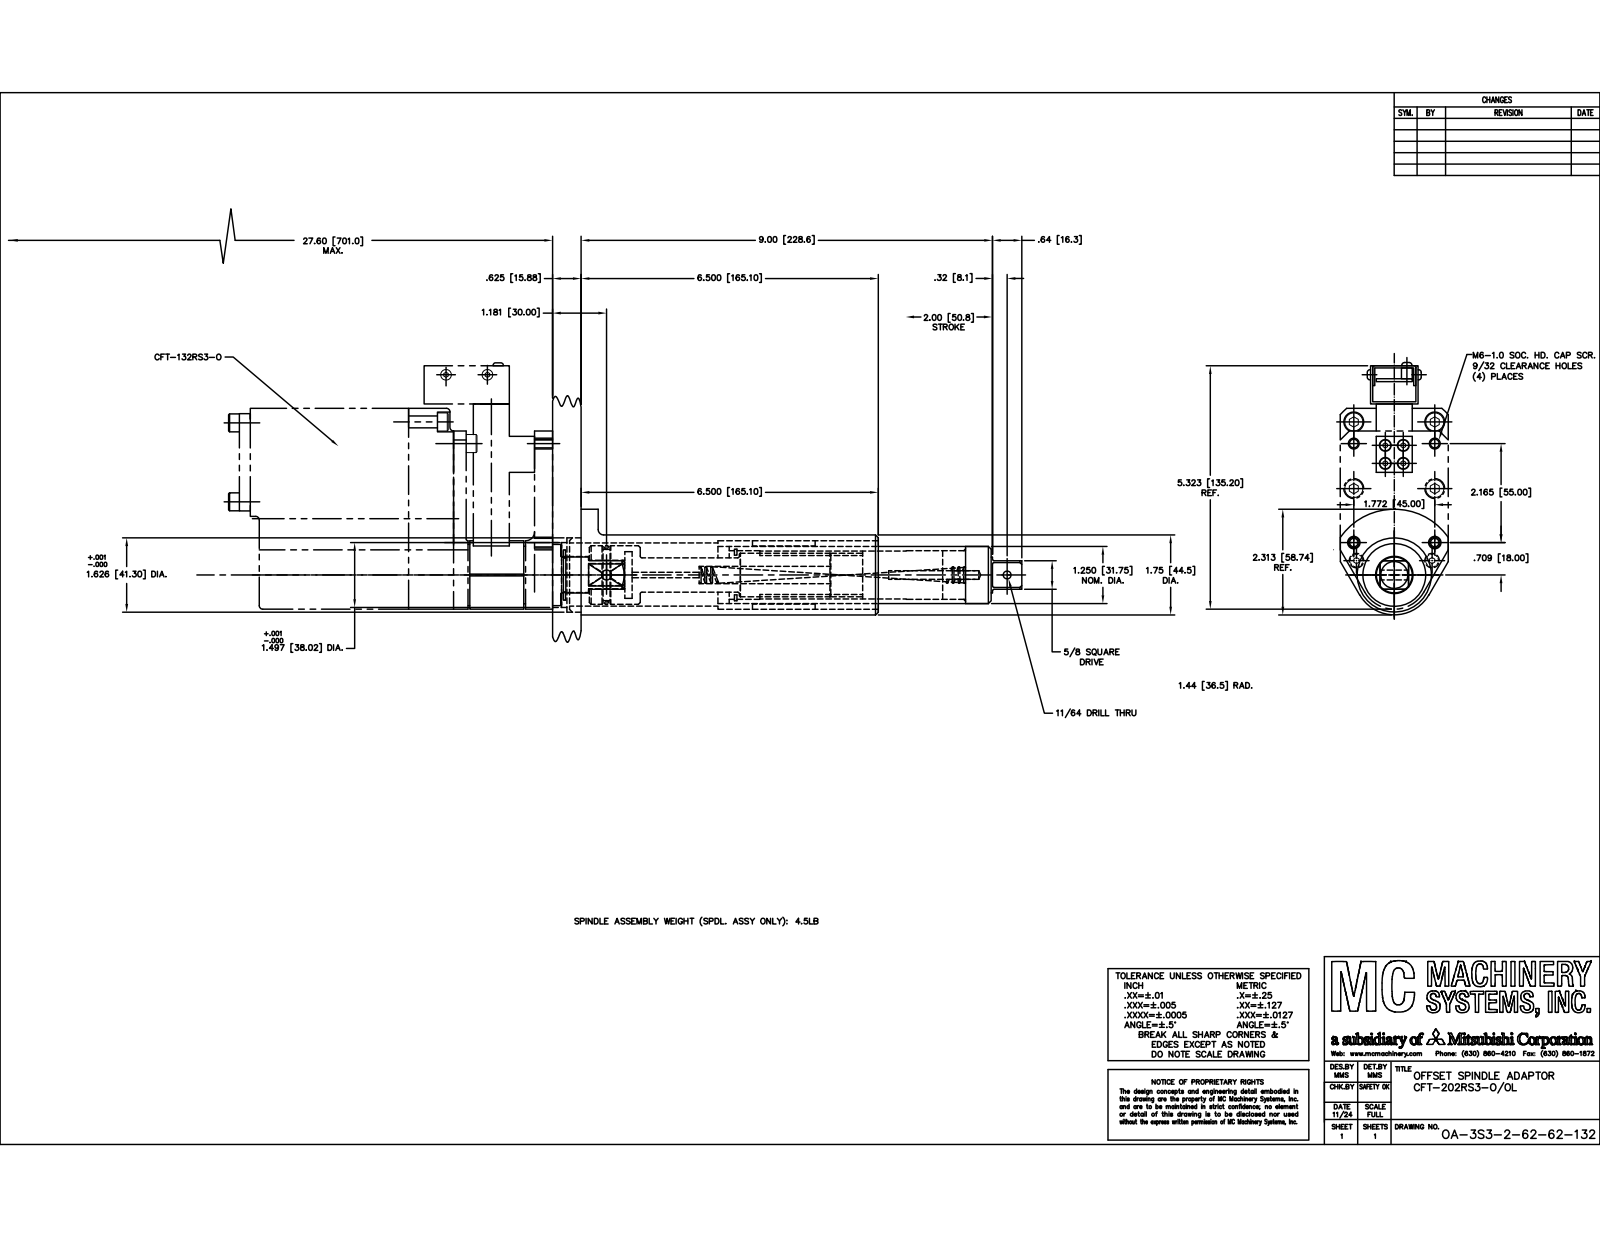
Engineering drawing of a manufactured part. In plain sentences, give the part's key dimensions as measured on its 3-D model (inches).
The part is named "OA-3S3-2-62-62-132; SA-036; SA-358H; R-6-12-6.50-20-1". Its 3-D file was written by "SolidWorks 2015 (CONFIG_CONTROL_DESIGN)". It is 3 solids with 113 faces: 37 planar, 55 cylindrical and 21 other. Overall it measures 9.87 by 2.36 by 2.31 inches. Its volume is 11.54 cubic inches and its surface area 139.8 square inches. Round holes: 2 of diameter 0.277, 1 of diameter 0.094, 1 of diameter 0.125, 1 of diameter 0.203, 1 of diameter 0.25, 1 of diameter 0.375, 1 of diameter 0.9, 1 of diameter 1.06, 1 of diameter 1.13, 1 of diameter 1.375, 1 of diameter 1.5. Round bosses or shafts: 1 of diameter 1.75, 1 of diameter 1.625, 1 of diameter 1.25, 1 of diameter 1.125, 1 of diameter 1, 1 of diameter 0.95, 1 of diameter 0.834, 1 of diameter 0.75. Partial cylindrical surfaces (rounded edges, fillets, slot ends): 4 of radius 0.047, 1 of radius 0.419, 1 of radius 1.44. The main face-to-face distances are 0.375, 0.627, 3.12, 0.625, 7.86, 7.485, 6.5, 2.745, 4.74, 0.872. The hole center spacings are 1.135, 1.772, 8.868.
